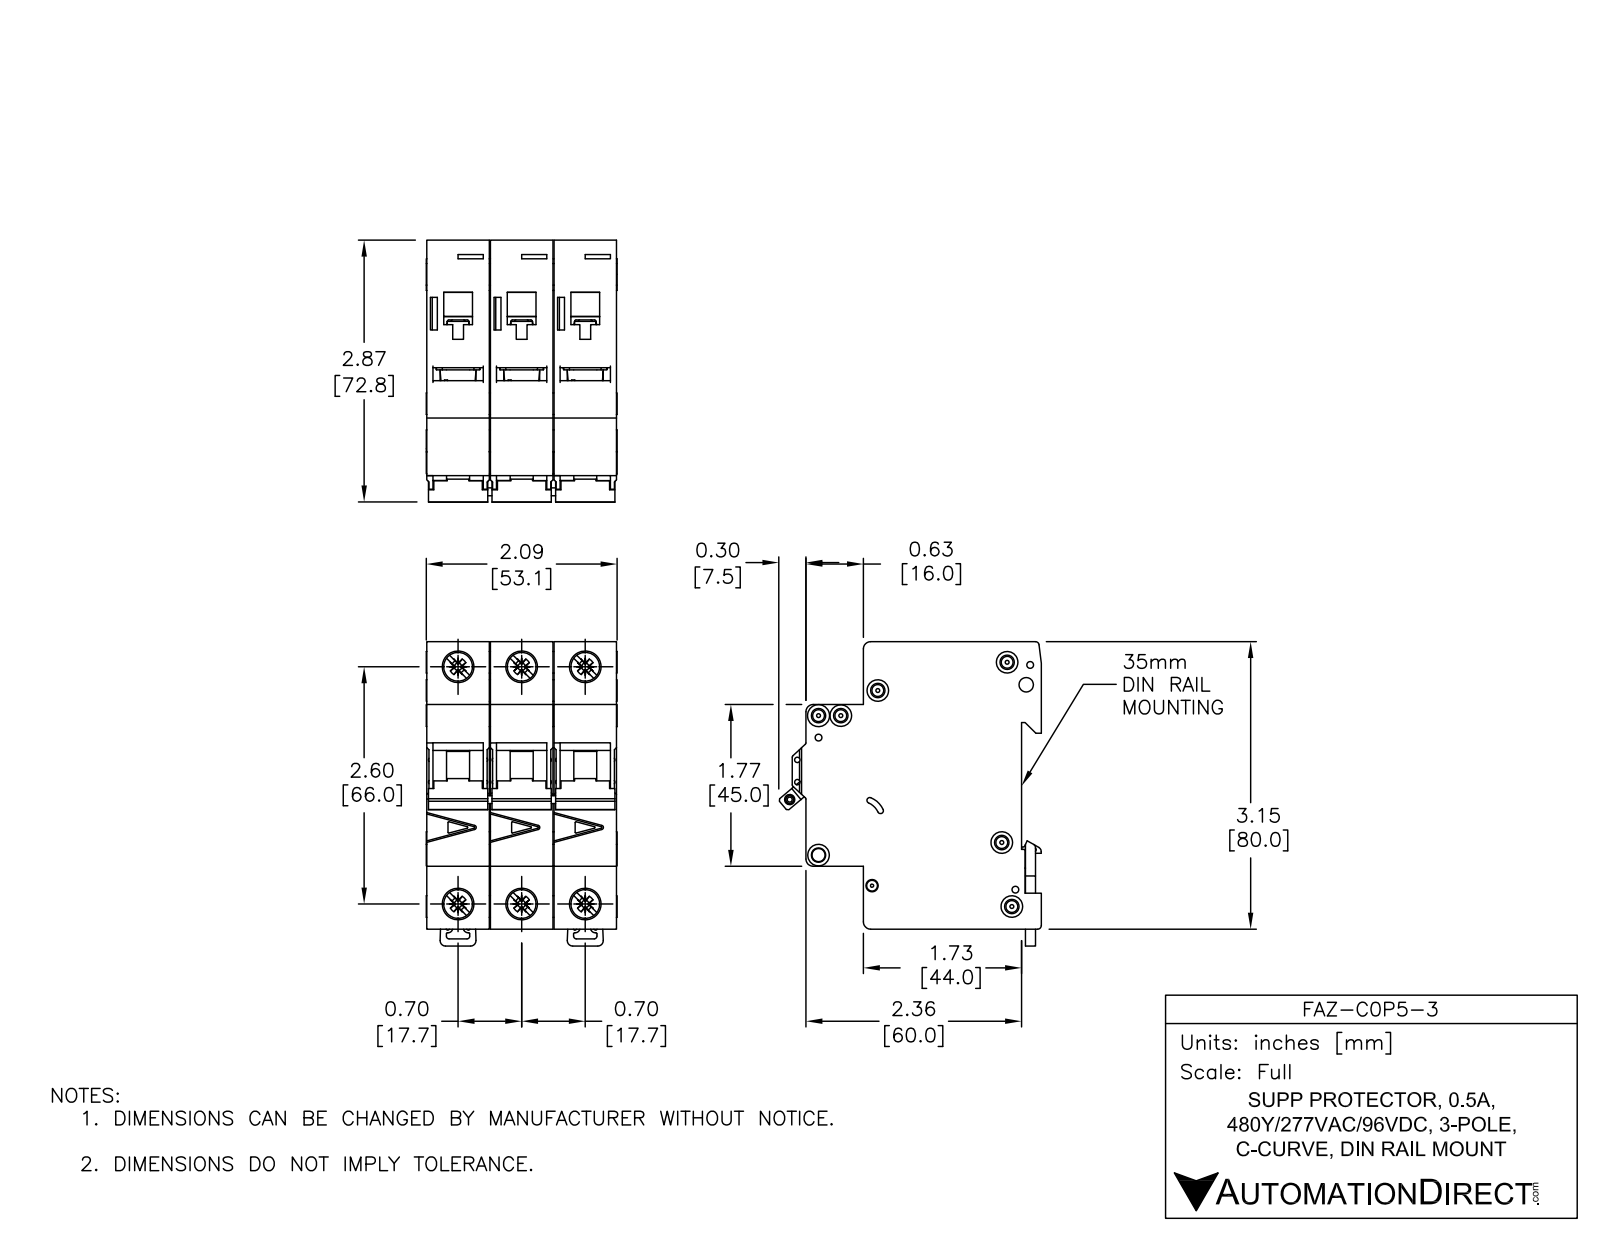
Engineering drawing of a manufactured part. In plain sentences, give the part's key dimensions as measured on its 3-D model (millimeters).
The part is named "FAZ-C0P5-3". Its 3-D file was written by "SolidWorks 2014 (AUTOMOTIVE_DESIGN)". It is 11 solids with 1650 faces: 697 planar, 590 cylindrical and 363 other. Overall it measures 84.78 by 73.04 by 53.1 millimeters. Its volume is 224 680 cubic millimeters and its surface area 58 052 square millimeters. Round holes: 6 of diameter 3.6, 4 of diameter 8.2, 3 of diameter 1.9, 2 of diameter 1.09, 2 of diameter 1.5, 2 of diameter 4, 2 of diameter 7.15, 1 of diameter 2.15, 1 of diameter 2.2, 1 of diameter 2.55, 1 of diameter 3.3, 1 of diameter 3.4. Round bosses or shafts: 4 of diameter 6, 3 of diameter 2.5, 2 of diameter 8.2. Partial cylindrical surfaces (rounded edges, fillets, slot ends): 68 of radius 0.25, 25 of radius 0.5, 12 of radius 1, 12 of radius 2, 11 of radius 0.2, 3 of radius 1.8, 2 of radius 0.8, 2 of radius 3. The main face-to-face distances are 17.7, 17.5, 35.4, 35.2, 52.9, 17.9, 79.48, 5.5, 49.5, 44. The hole center spacings are 17.7, 68.33, 66, 6.2, 13.64, 35.4, 74.89, 4.81.
